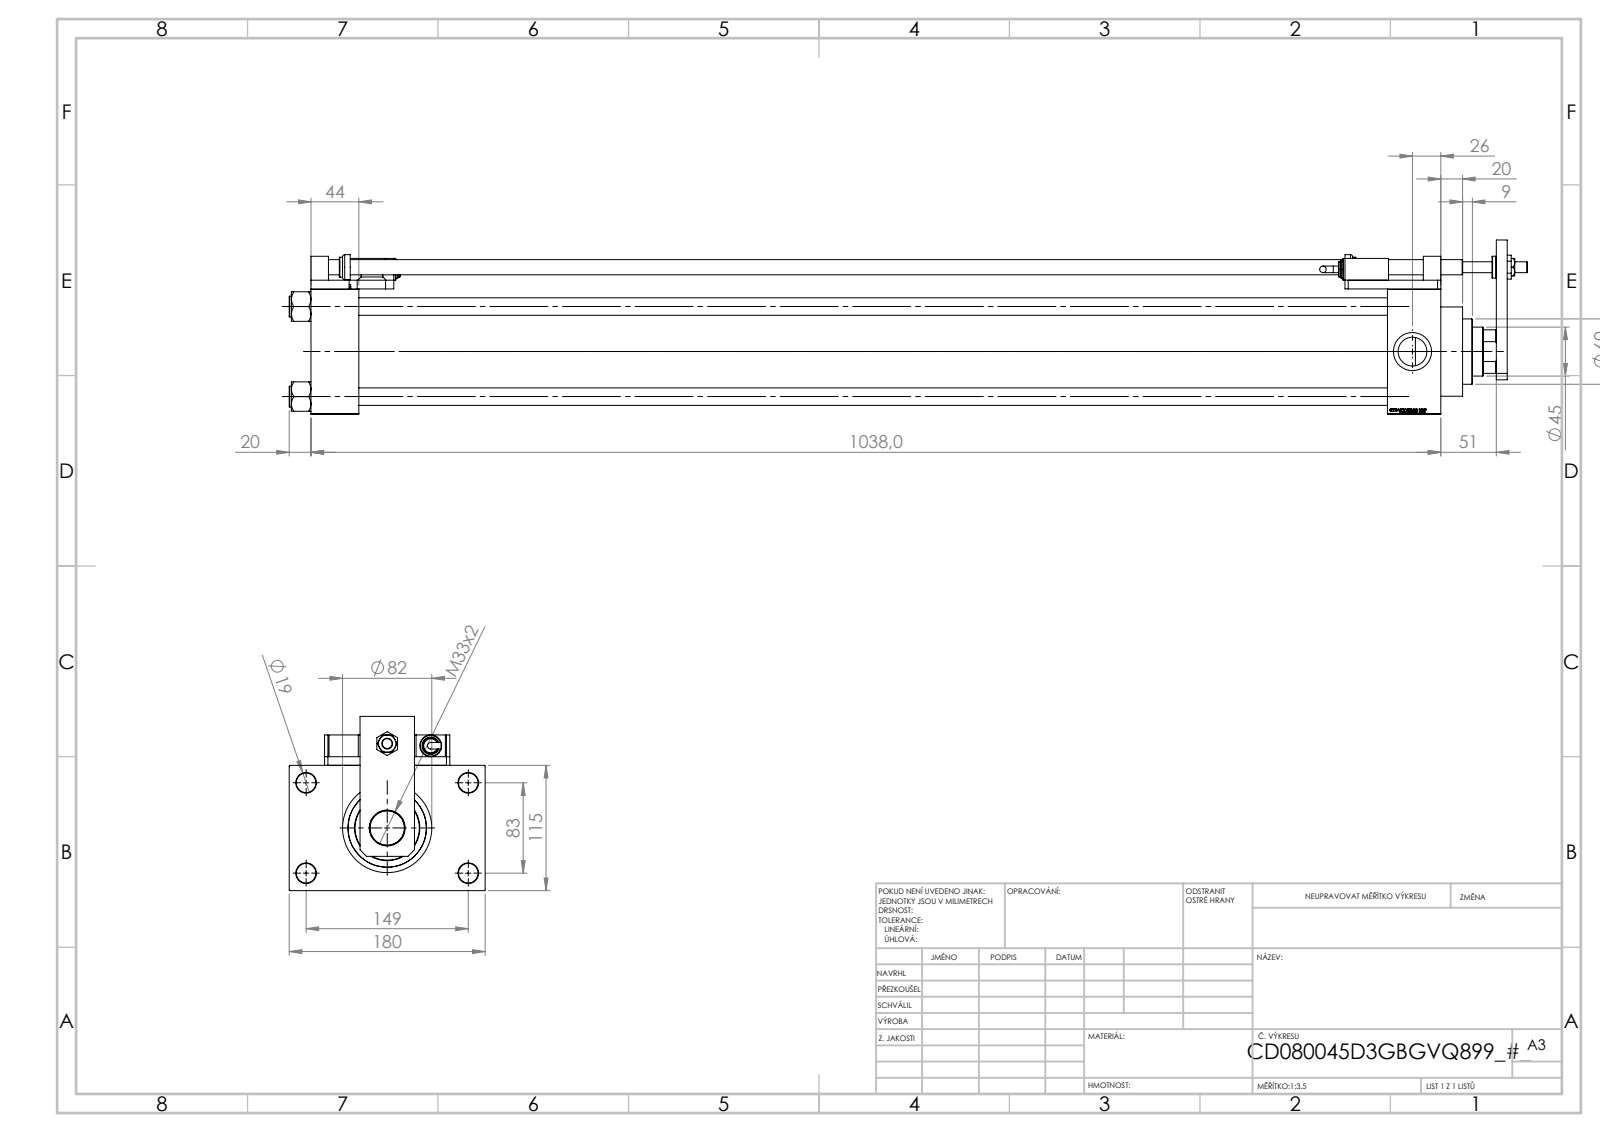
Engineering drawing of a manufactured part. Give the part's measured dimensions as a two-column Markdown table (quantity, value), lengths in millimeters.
| quantity | value |
| --- | --- |
| part name | Zatka_pro_OIL_PORT; V215CD_SWITCH_Q_MAGNET; V215CD_VCP_D; V215CD_D_Body (+8 more) |
| STEP written by | SolidWorks 2019 (CONFIG_CONTROL_DESIGN) |
| units | millimeters |
| bodies | 26 solids, 1480 faces (714 planar, 167 cylindrical, 599 other) |
| overall size | 1137.5 × 180 × 160 |
| volume | 5 210 000 mm³ |
| surface area | 1 198 000 mm² |
| round holes (diameter × count) | 8.5 × 4, 13.5 × 4, 16 × 4, 18 × 4, 26.44 × 4, 35 × 4, 7 × 3, 10 × 1, 14 × 1, 31.5 × 1, 33 × 1, 45 × 1 |
| round bosses / shafts (diameter × count) | 19 × 4, 20 × 3, 16 × 2, 14 × 2, 6 × 2, 86 × 1, 82 × 1, 60 × 1 |
| partial cylindrical surfaces (radius × count) | 7.5 × 4, 22 × 1 |
| main face-to-face distances | 115, 8, 49, 44, 994, 1038, 989, 945, 123, 32.5 |
| hole center spacings | 33.15, 58.48, 82.7, 85.28, 89.24, 115.85, 142.43, 21.26 |
